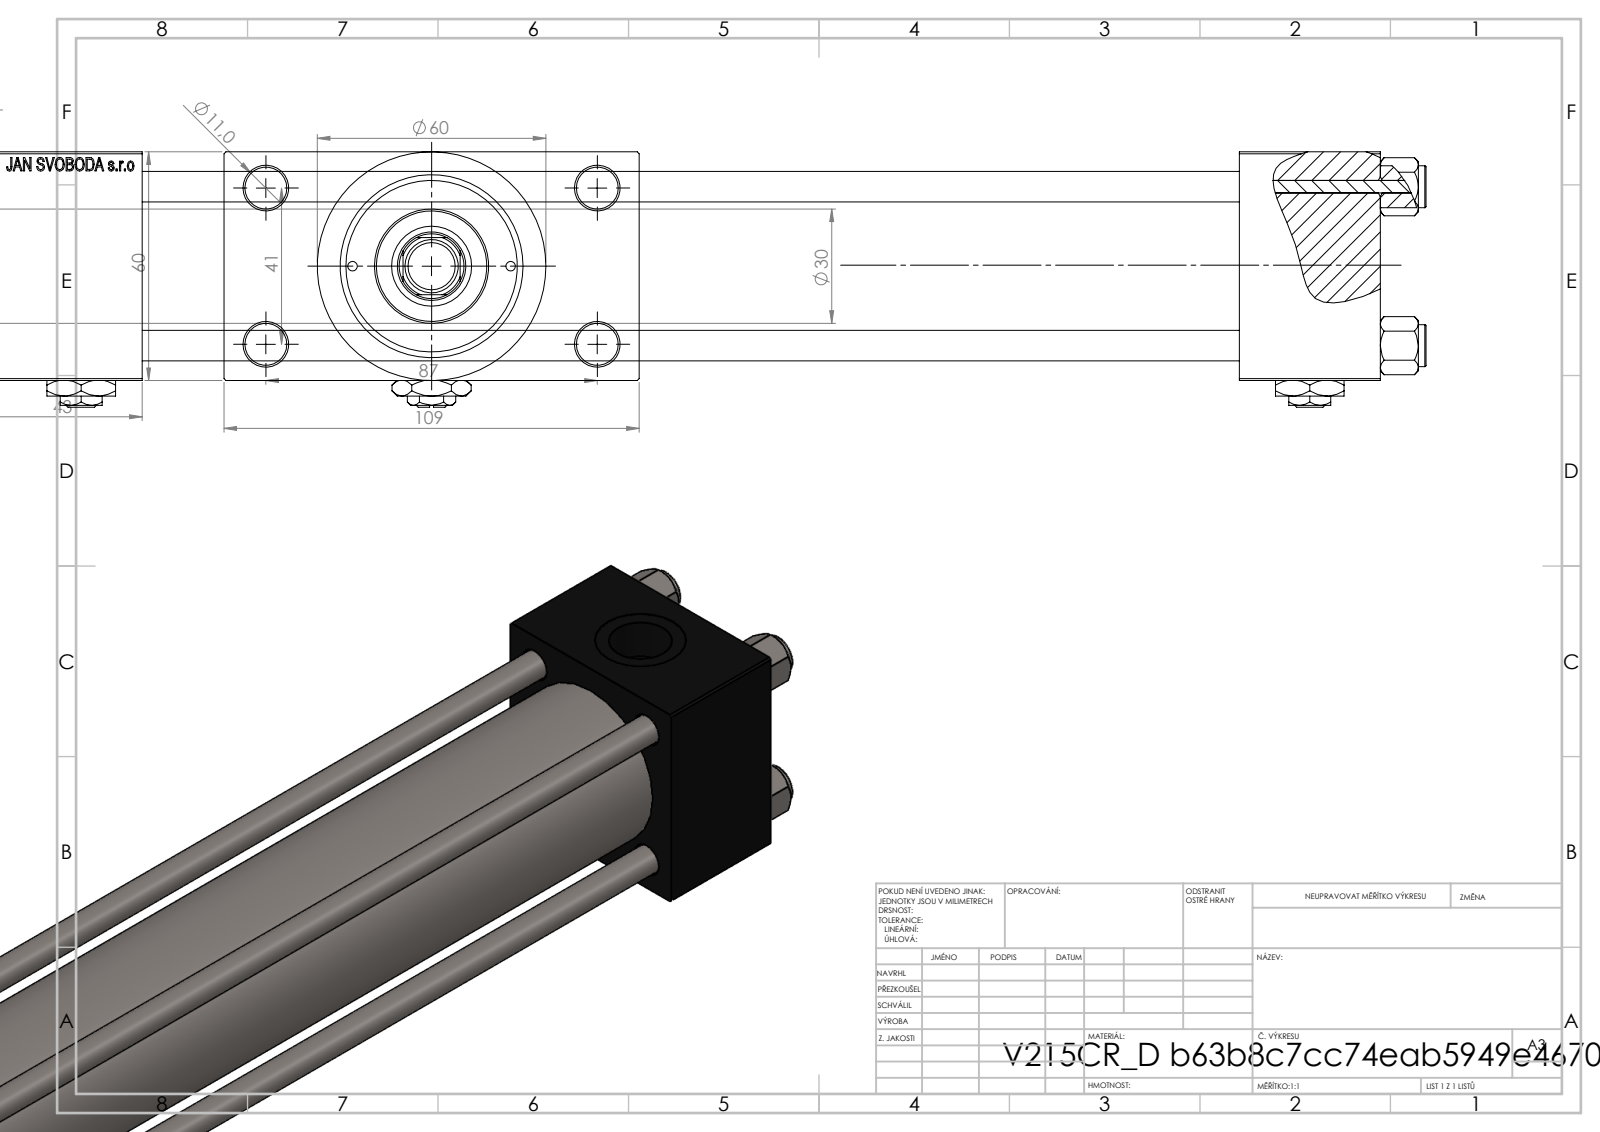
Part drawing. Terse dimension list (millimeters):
name: V215CR_D_TYCINKA; ROD_END_AH; V215CR_VCP_D; V215CR_D_Body (+3 more)
written by: SolidWorks 2019 (CONFIG_CONTROL_DESIGN)
unit: mm
bodies: 14 solids, 1228 faces (552 planar, 108 cylindrical, 568 other)
size: 433 × 109 × 67
volume: 716 035 mm³; area: 223 267 mm²
holes: 4× ⌀8, 4× ⌀11, 2× ⌀2.5, 2× ⌀7, 2× ⌀16.66, 2× ⌀24, 1× ⌀8.5, 1× ⌀18, 1× ⌀21, 1× ⌀31, 1× ⌀40, 1× ⌀45
bosses: 4× ⌀11, 1× ⌀60, 1× ⌀46, 1× ⌀30, 1× ⌀14, 1× ⌀12
rounds: 1× R8.5
face distances: 60, 24.5, 84.5, 288, 37, 325, 43, 368, 331, 109
hole spacings: 20.85, 22.65, 29.49, 30.62, 41.7, 46.53, 47.15, 48.09
